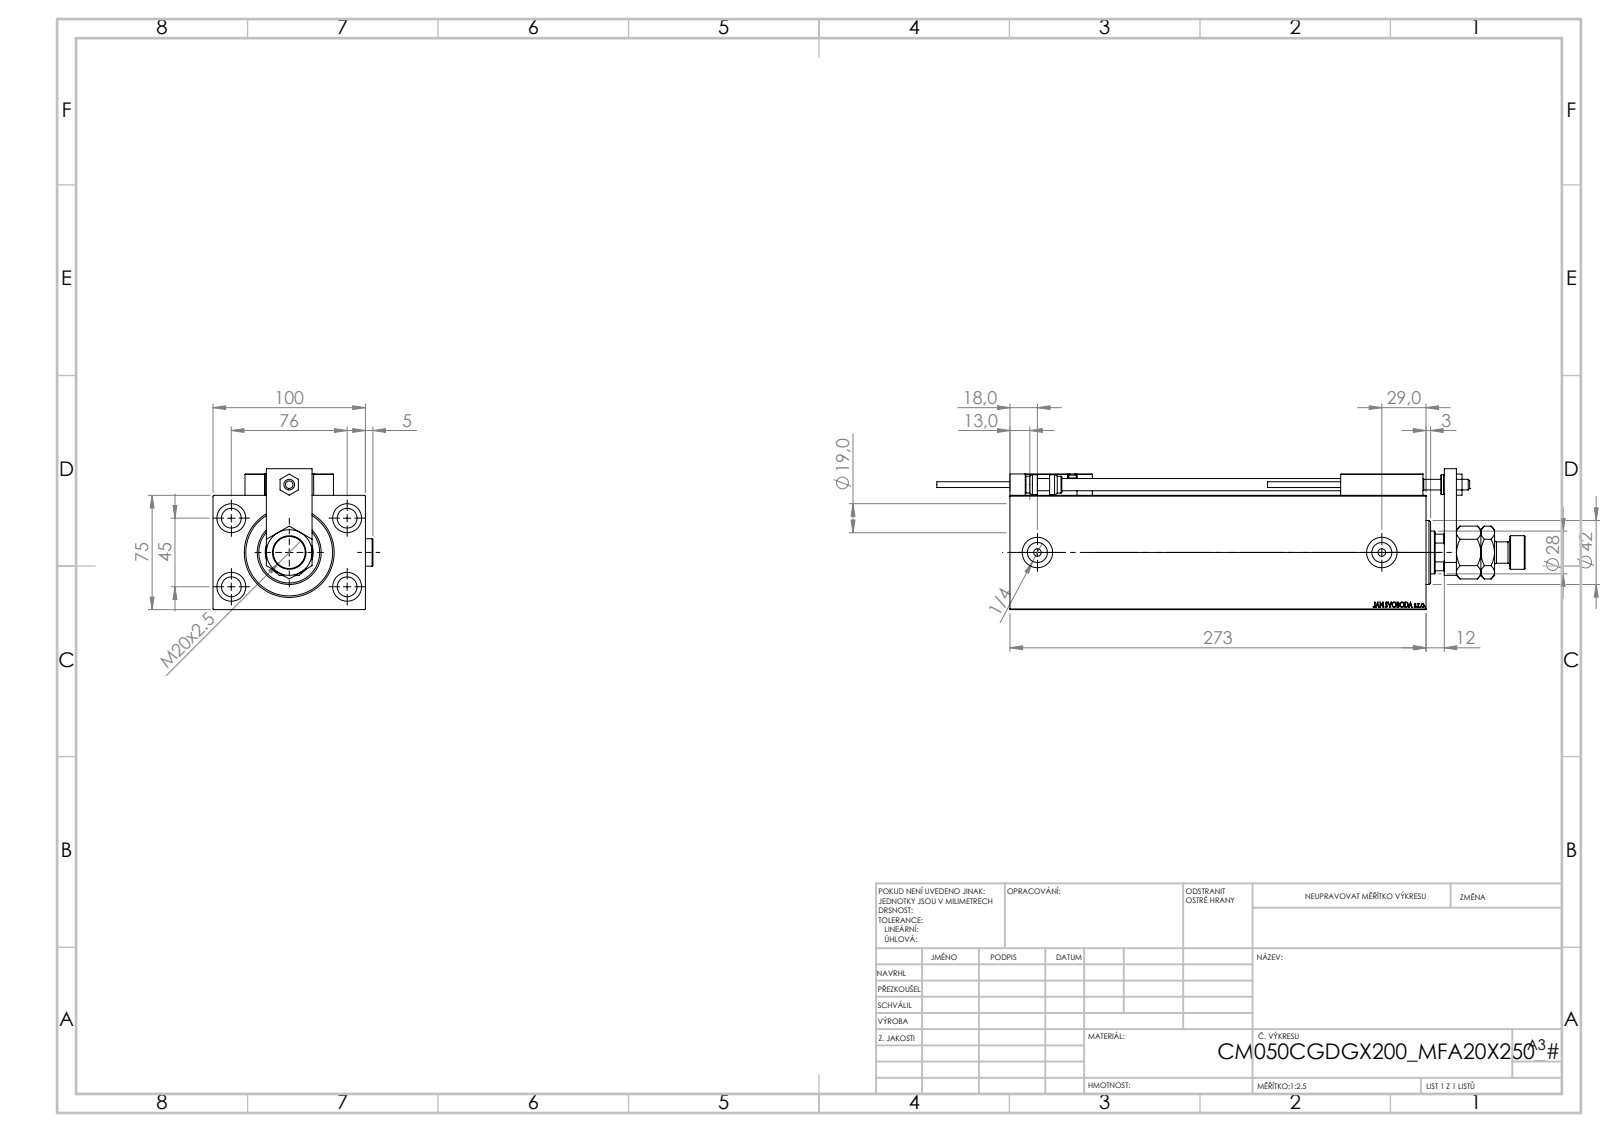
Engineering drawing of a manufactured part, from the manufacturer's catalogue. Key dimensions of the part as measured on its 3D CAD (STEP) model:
Part name (STEP PRODUCT): SWITCH_X_FRONT_BACK; SWITCH DIM B,W; Zatka_OIL_PORT; ALLEN BOLT D8 (+7 more)
STEP written by: SolidWorks 2019 (CONFIG_CONTROL_DESIGN)
Units: millimetres
Bodies: 26 solids, 1391 faces (611 planar, 210 cylindrical, 570 other)
Overall size (bounding box): 386 × 104.9 × 92.5
Volume: 1 702 000 mm³ · Surface area: 277 734 mm²
Round holes (diameter × count): ⌀8 ×5, ⌀3.2 ×4, ⌀4 ×4, ⌀5 ×4, ⌀13 ×4, ⌀19 ×4, ⌀20 ×3, ⌀13.16 ×2, ⌀7 ×1, ⌀18.5 ×1, ⌀28 ×1, ⌀31.5 ×1
Round bosses / shafts (diameter × count): ⌀18 ×2, ⌀5 ×2, ⌀3.8 ×2, ⌀42 ×1, ⌀22 ×1, ⌀14 ×1, ⌀13 ×1, ⌀11 ×1
Partial cylindrical surfaces — rounded edges, fillets, slot ends (radius × count): R0.3 ×30, R3 ×2, R13.5 ×1
Main face-to-face distances: 75, 100, 14, 273, 12, 259, 20, 8, 24, 25
Hole centre spacings: 44.16, 11.37, 20, 29.59, 29.69, 36.06, 42.19, 43.91
